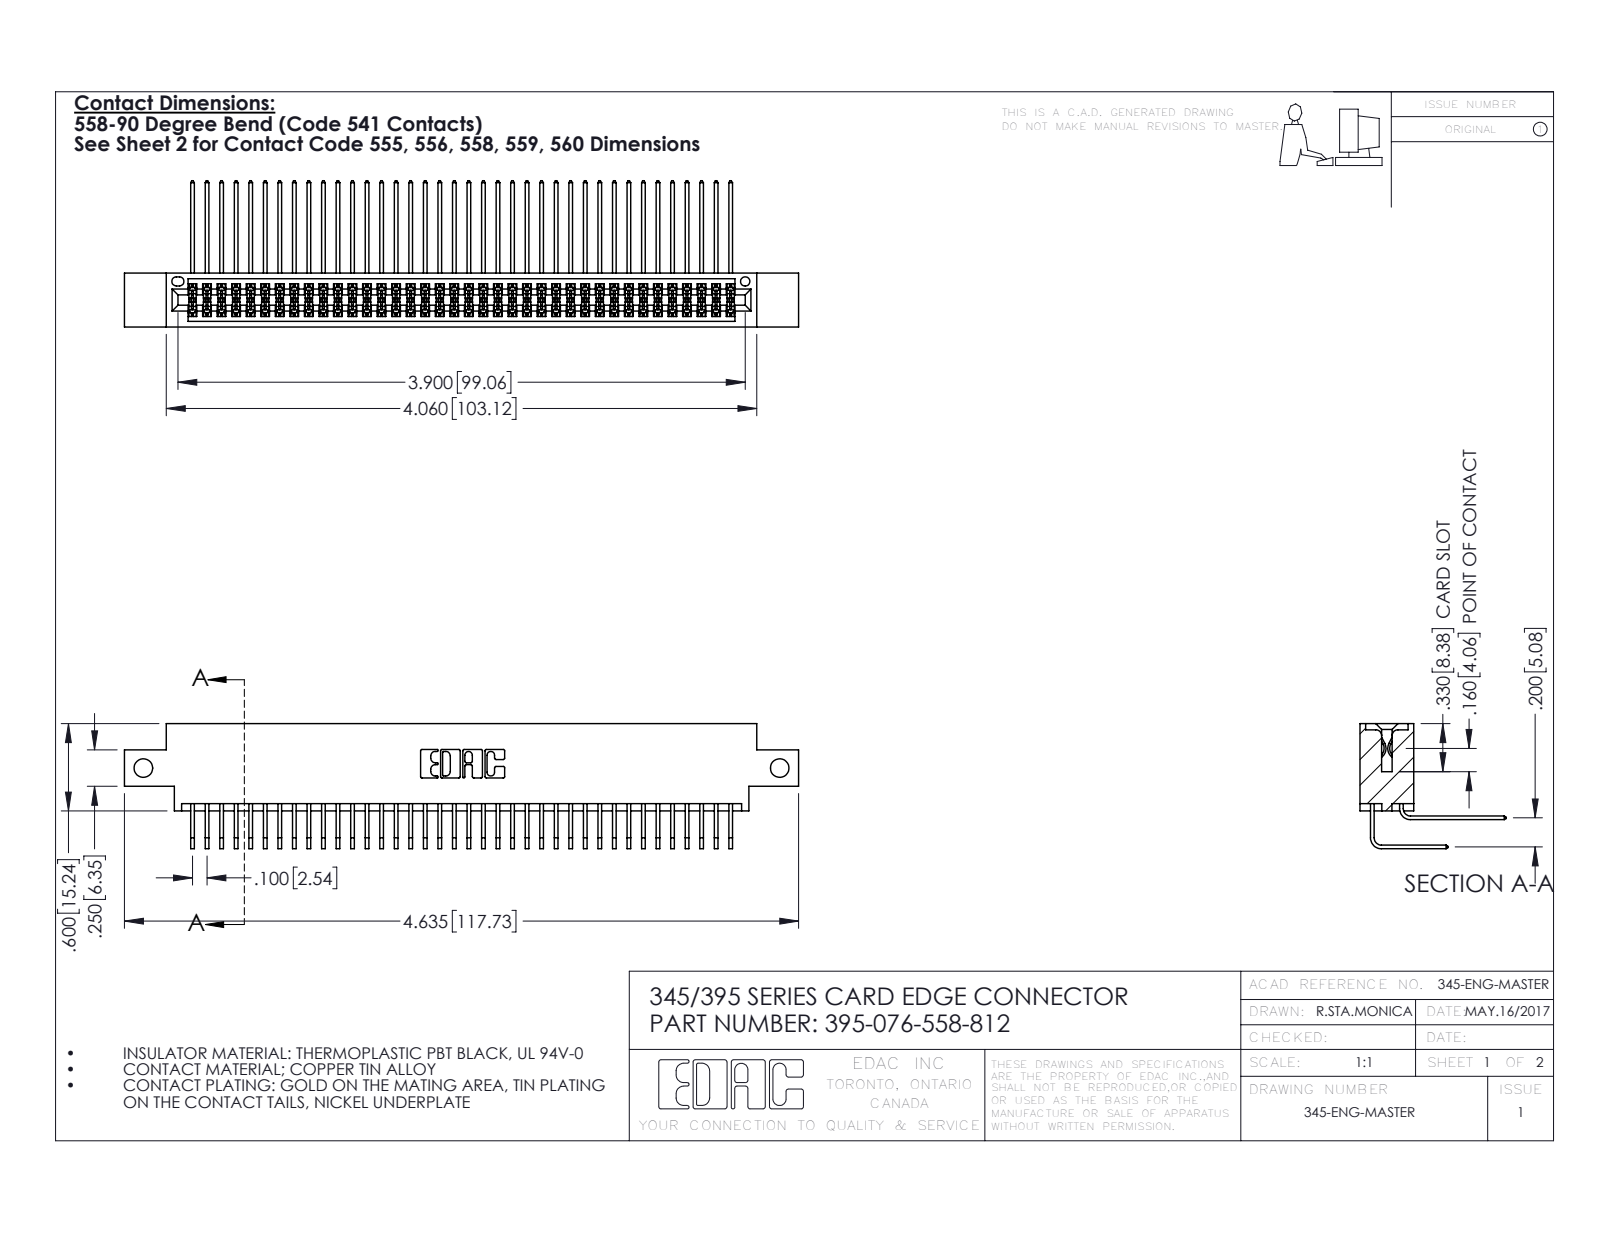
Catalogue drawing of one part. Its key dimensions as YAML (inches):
part_name: "395-076-558-812; 345-292-001_558 559 Tail - 1; 345-292-001_558 Tail - 2; 345 Part_0.170 Offset - Side Mount"
step_written_by: "SolidWorks 2016 (CONFIG_CONTROL_DESIGN)"
units: inches
bodies: {solids: 77, faces: 4082, planar: 2744, cylindrical: 1338, other: 0}
overall_size: [4.635, 1.005, 0.859]
volume: 0.71
surface_area: 29.75
round_holes:
  - {diameter: 0.128, count: 2}
  - {diameter: 0.064, count: 1}
partial_cylinders:
  - {radius: 0.006, count: 114}
  - {radius: 0.01, count: 22}
  - {radius: 0.007, count: 6}
  - {radius: 0.031, count: 6}
  - {radius: 0.026, count: 3}
  - {radius: 0.014, count: 2}
  - {radius: 0.019, count: 2}
  - {radius: 0.022, count: 2}
face_to_face_distances: [0.072, 0.298, 0.2, 0.37, 0.098, 0.272, 0.025, 0.225, 0.175, 0.025]
hole_center_spacings: [4.375]
